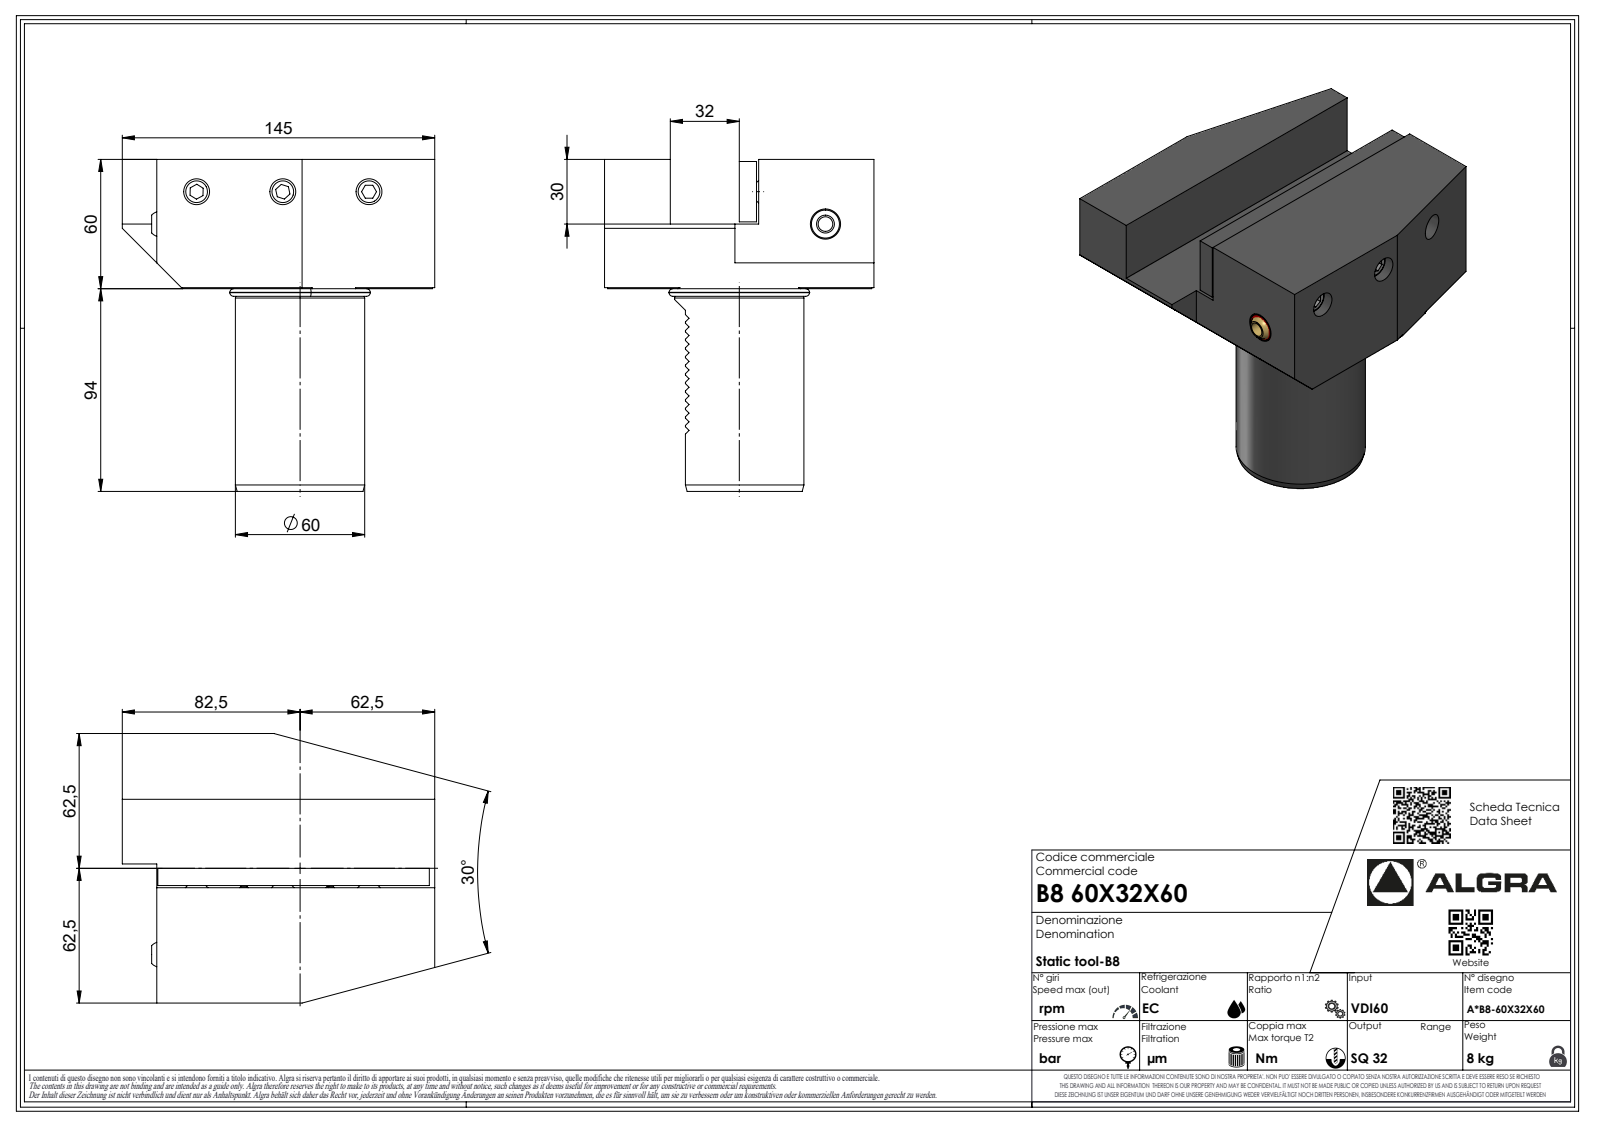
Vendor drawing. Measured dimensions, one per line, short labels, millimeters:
name: B860X32X60
written by: SolidWorks 2023 (AUTOMOTIVE_DESIGN)
unit: mm
bodies: 1 solid, 351 faces (226 planar, 32 cylindrical, 93 other)
size: 154 × 145 × 125
volume: 1 035 000 mm³; area: 87 687 mm²
holes: 1× ⌀2.1
bosses: 1× ⌀65.39, 1× ⌀60, 1× ⌀58.7, 1× ⌀6.37, 1× ⌀1.7
rounds: 7× R0.33, 7× R0.52, 7× R3.7, 1× R0.21, 1× R61.5
face distances: 30, 60, 62.5, 94.5, 30.5, 125, 32, 129, 154, 124
